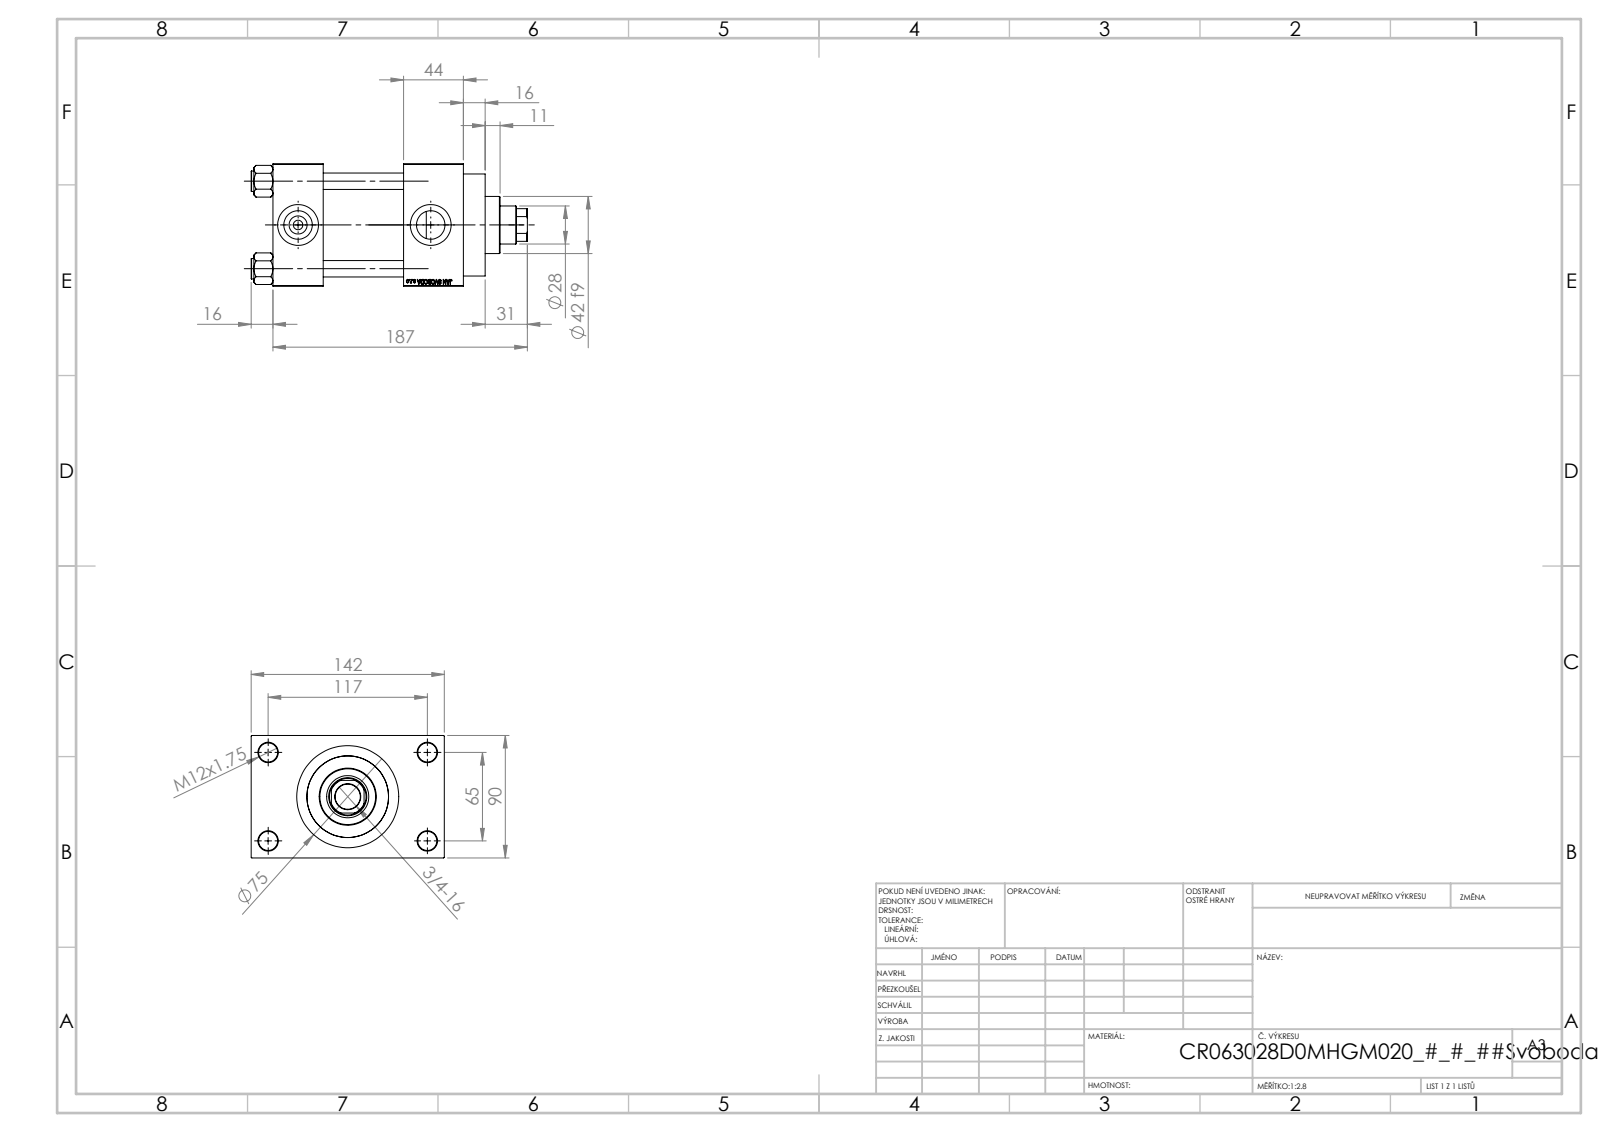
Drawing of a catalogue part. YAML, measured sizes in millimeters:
part_name: "NUT_M5_D; V215_VC_A; V215CR_D_Body; V215CR_VCP_D (+1 more)"
step_written_by: "SolidWorks 2019 (CONFIG_CONTROL_DESIGN)"
units: millimeters
bodies: {solids: 11, faces: 1103, planar: 497, cylindrical: 88, other: 518}
overall_size: [203, 142, 90]
volume: 1096000
surface_area: 200314
round_holes:
  - {diameter: 12, count: 4}
  - {diameter: 14, count: 4}
  - {diameter: 7, count: 2}
  - {diameter: 20.96, count: 2}
  - {diameter: 30, count: 2}
  - {diameter: 18.5, count: 1}
  - {diameter: 28, count: 1}
  - {diameter: 31, count: 1}
  - {diameter: 50, count: 1}
  - {diameter: 60, count: 1}
  - {diameter: 63, count: 1}
round_bosses_or_shafts:
  - {diameter: 15, count: 4}
  - {diameter: 75, count: 1}
  - {diameter: 69, count: 1}
  - {diameter: 42, count: 1}
partial_cylinders:
  - {radius: 13.5, count: 1}
face_to_face_distances: [90, 59, 37, 96, 140, 103, 44, 26, 116, 16]
hole_center_spacings: [26.35, 45.47, 64.3, 66.92, 69.81, 90.65, 111.34, 65]
